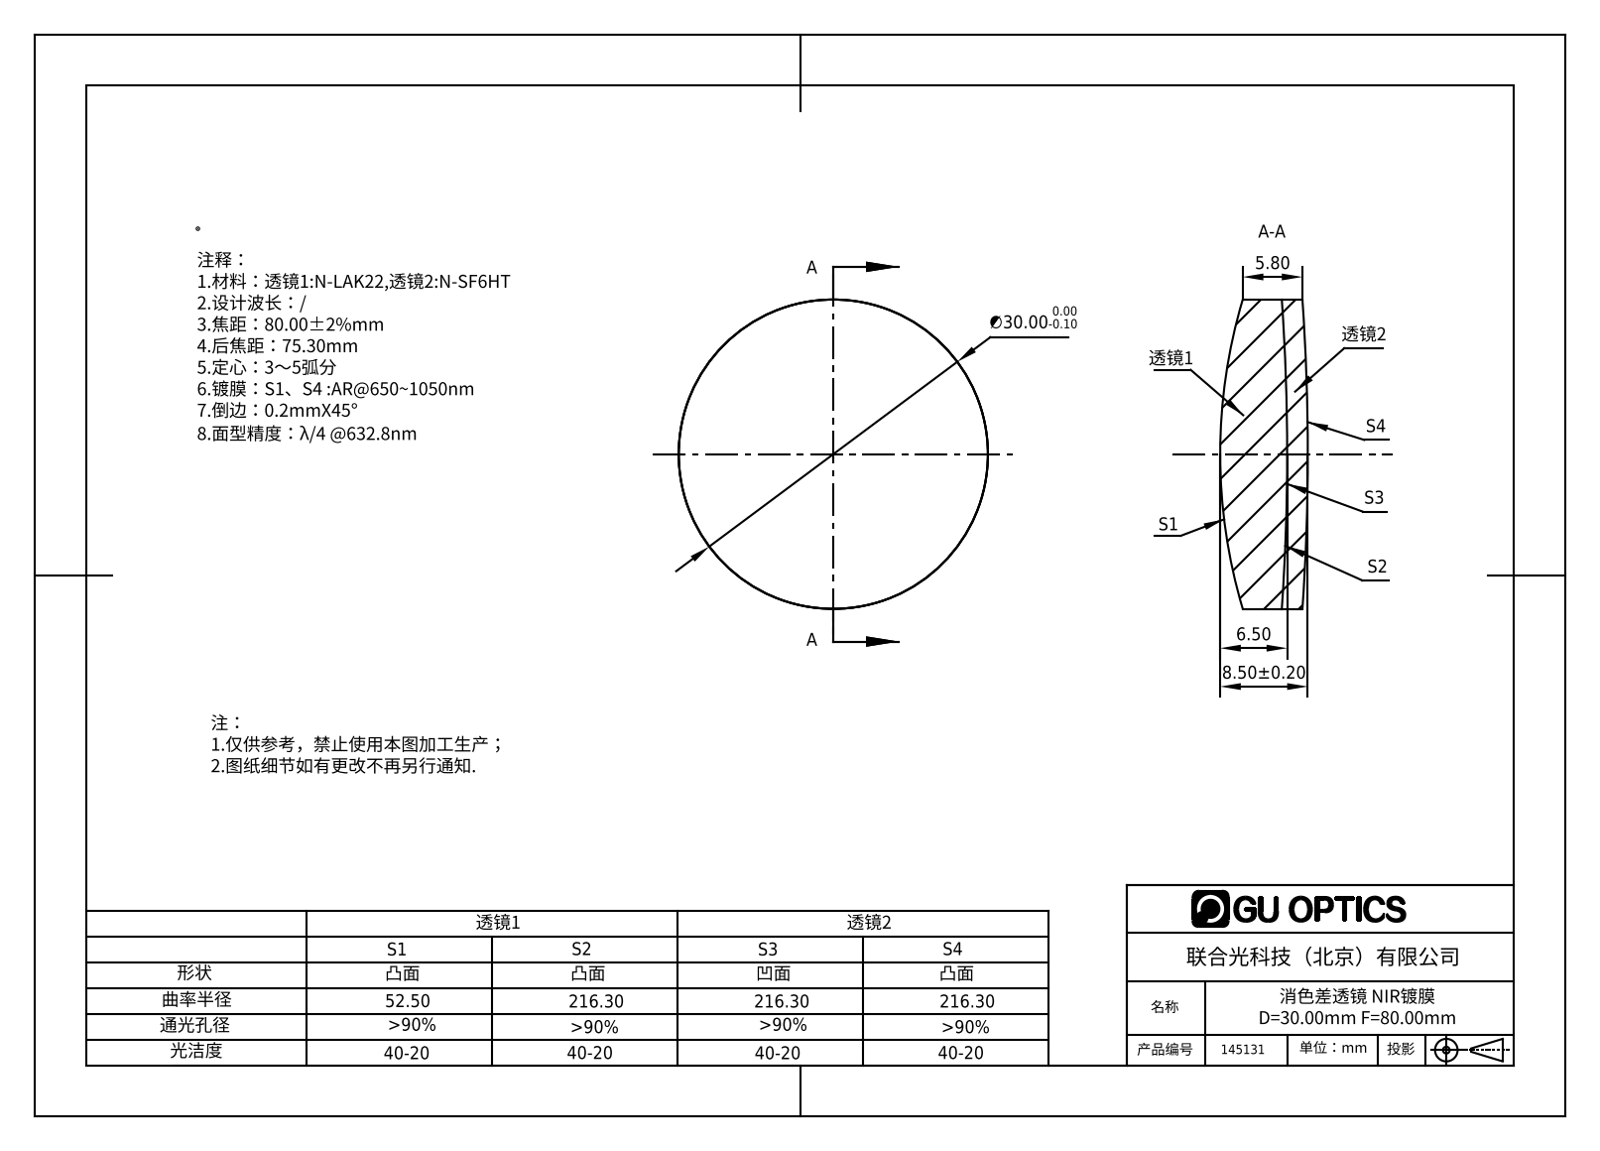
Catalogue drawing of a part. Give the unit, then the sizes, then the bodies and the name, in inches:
Units: inches
Overall size (bounding box): 1.181 × 1.181 × 0.335
Round bosses / shafts (diameter × count): ⌀1.181 ×1
Volume: 0.309 in³ · Surface area: 5.256 in²
Bodies: 2 solids, 12 faces (0 planar, 4 cylindrical, 8 other)
Part name (STEP PRODUCT): 145131
STEP written by: SolidWorks 2016 (AUTOMOTIVE_DESIGN)
